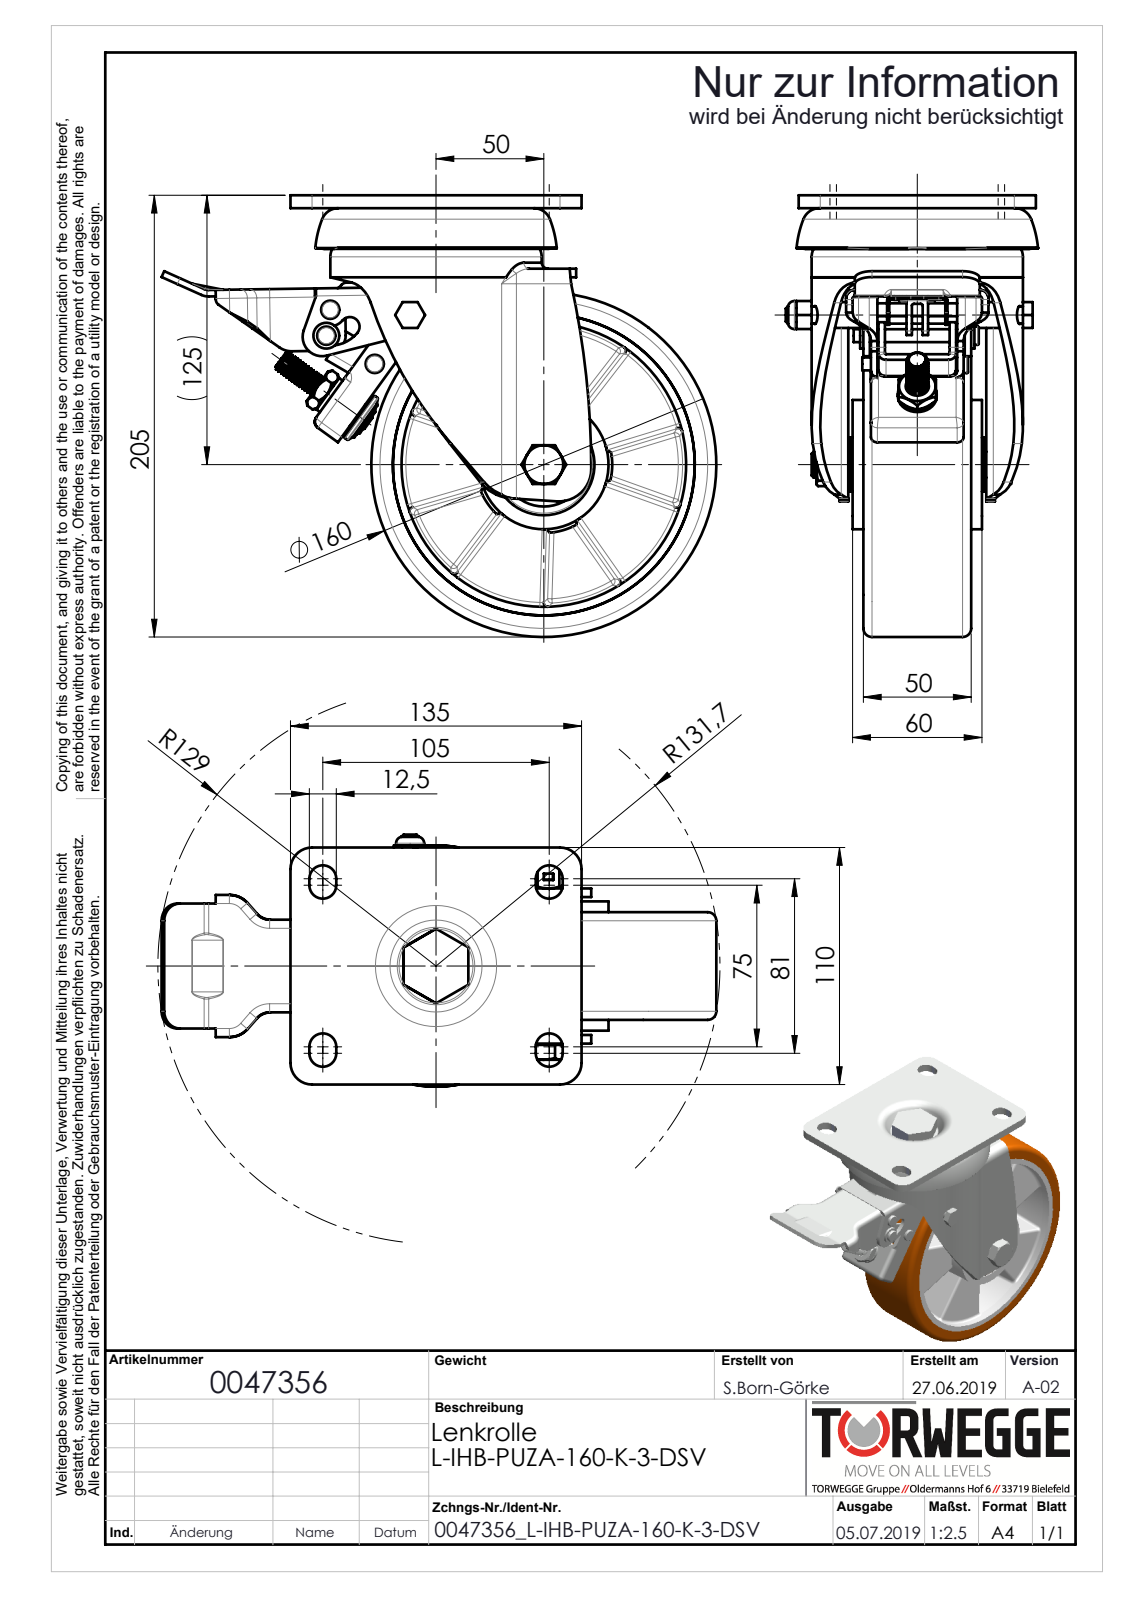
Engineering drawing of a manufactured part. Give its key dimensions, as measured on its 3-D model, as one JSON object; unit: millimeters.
{"part_name": "0047356_L-IHB-PUZA-160-K-3-DSV_(A-02)", "step_written_by": "SolidWorks 2018 (AUTOMOTIVE_DESIGN)", "units": "millimeters", "bodies": {"solids": 0, "faces": 1231, "planar": 369, "cylindrical": 477, "other": 385}, "overall_size": [257.29, 205, 117], "round_holes": [[4, 3], [6.5, 3], [20.5, 2], [5, 1], [8, 1], [8.5, 1], [10.2, 1], [12, 1], [12.2, 1], [12.5, 1], [20, 1], [28.1, 1]], "round_bosses_or_shafts": [[8.5, 3], [6, 3], [24, 2], [20, 2], [18, 2], [12, 2], [160, 1], [98.01, 1]], "partial_cylinders_radius": [[2, 46], [1, 34], [3.5, 11], [6.25, 10], [4, 9], [0.5, 8], [3, 8], [8, 7]], "face_to_face_distances": [6, 4, 43.5, 17.5, 50.5, 3, 6.5, 10.5, 7, 46.5], "hole_center_spacings": [12.16, 26.01, 28, 32.51, 37.12, 40.03, 91.29, 93.08]}
